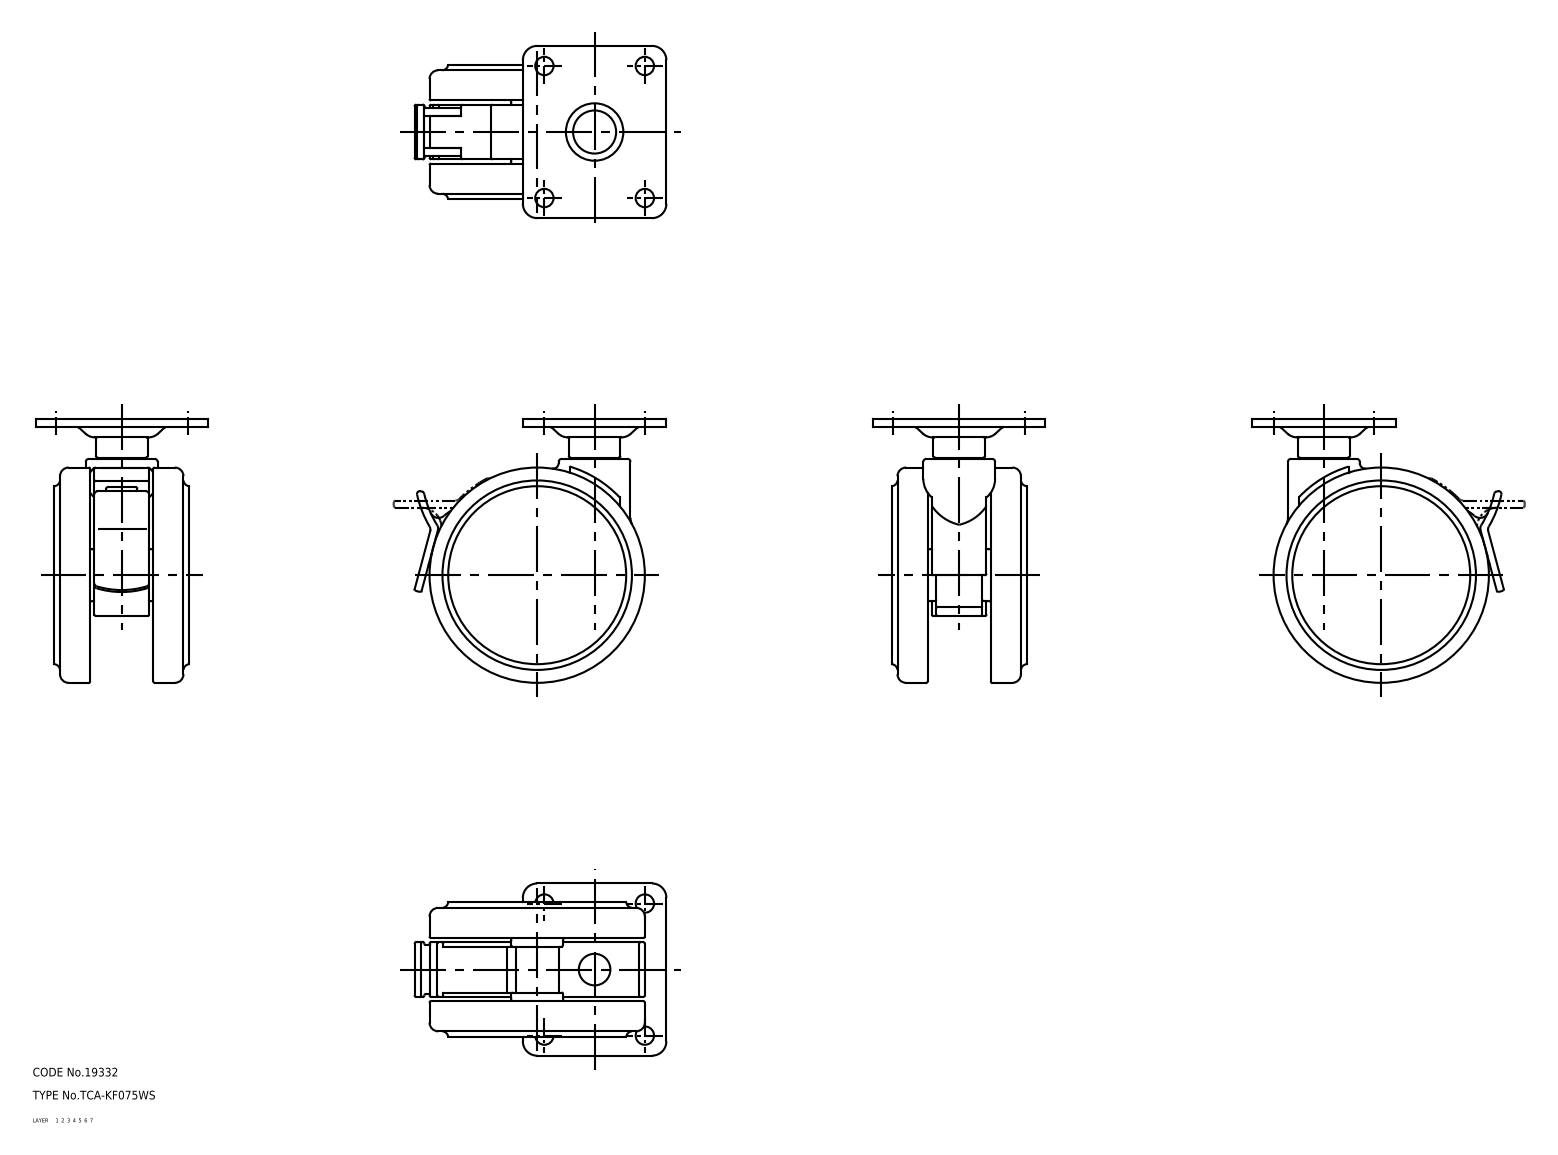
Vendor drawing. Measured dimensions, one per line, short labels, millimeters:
name: main shaft; wheel; wheel_mr; mounting plate (+2 more)
written by: SolidWorks 2015 (AUTOMOTIVE_DESIGN)
unit: mm
bodies: 6 solids, 284 faces (57 planar, 118 cylindrical, 109 other)
size: 92 × 87.75 × 60
volume: 163 851 mm³; area: 46 016 mm²
holes: 4× ⌀6.4, 1× ⌀6, 1× ⌀43
bosses: 2× ⌀18, 1× ⌀75, 1× ⌀25, 1× ⌀17, 1× ⌀15
rounds: 41× R0.5, 4× R5, 2× R1, 2× R2, 2× R3, 2× R35.5, 1× R2.89, 1× R7
face distances: 3, 12.5, 34.5, 1.5, 22, 14, 19, 20.5, 47, 33
hole spacings: 28.9, 35, 46, 57.8
